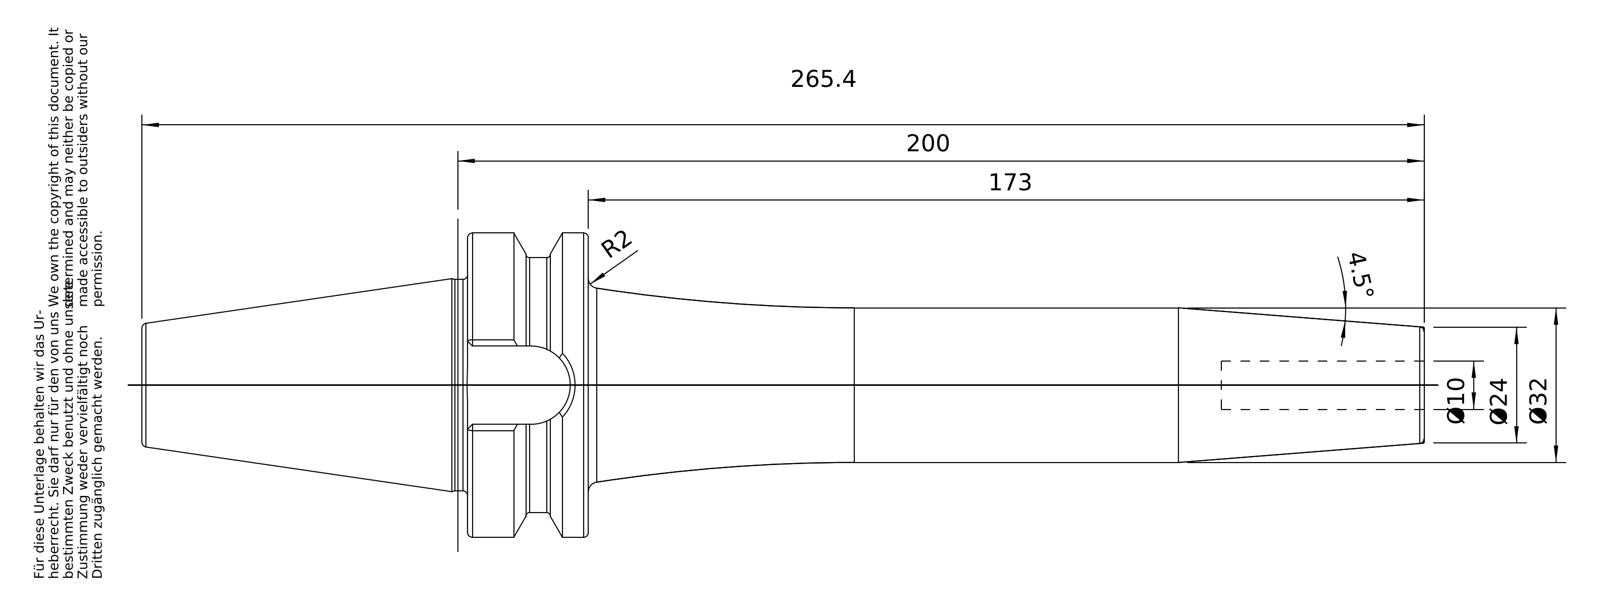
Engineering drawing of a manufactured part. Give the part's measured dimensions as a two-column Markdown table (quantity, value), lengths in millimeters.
| quantity | value |
| --- | --- |
| part name | 40-646-10 |
| STEP written by | PRO/ENGINEER BY PARAMETRIC TECHNOLOGY CORPORATION, 2010430 (CONFIG_CONTROL_DESIGN) |
| units | millimeters |
| bodies | 1 solid, 98 faces (26 planar, 22 cylindrical, 50 other) |
| overall size | 265.4 × 62.98 × 62.98 |
| volume | 261 320 mm³ |
| surface area | 39 496 mm² |
| round holes (diameter × count) | 10 × 1, 13.84 × 1, 17.01 × 1, 17.5 × 1 |
| round bosses / shafts (diameter × count) | 62.98 × 1, 52.75 × 1, 43.75 × 1, 32 × 1, 16.01 × 1 |
| partial cylindrical surfaces (radius × count) | 8.1 × 1 |
| main face-to-face distances | 25, 44.9, 198, 173, 16.2, 67.4, 92.4, 265.4, 223.4, 156 |
